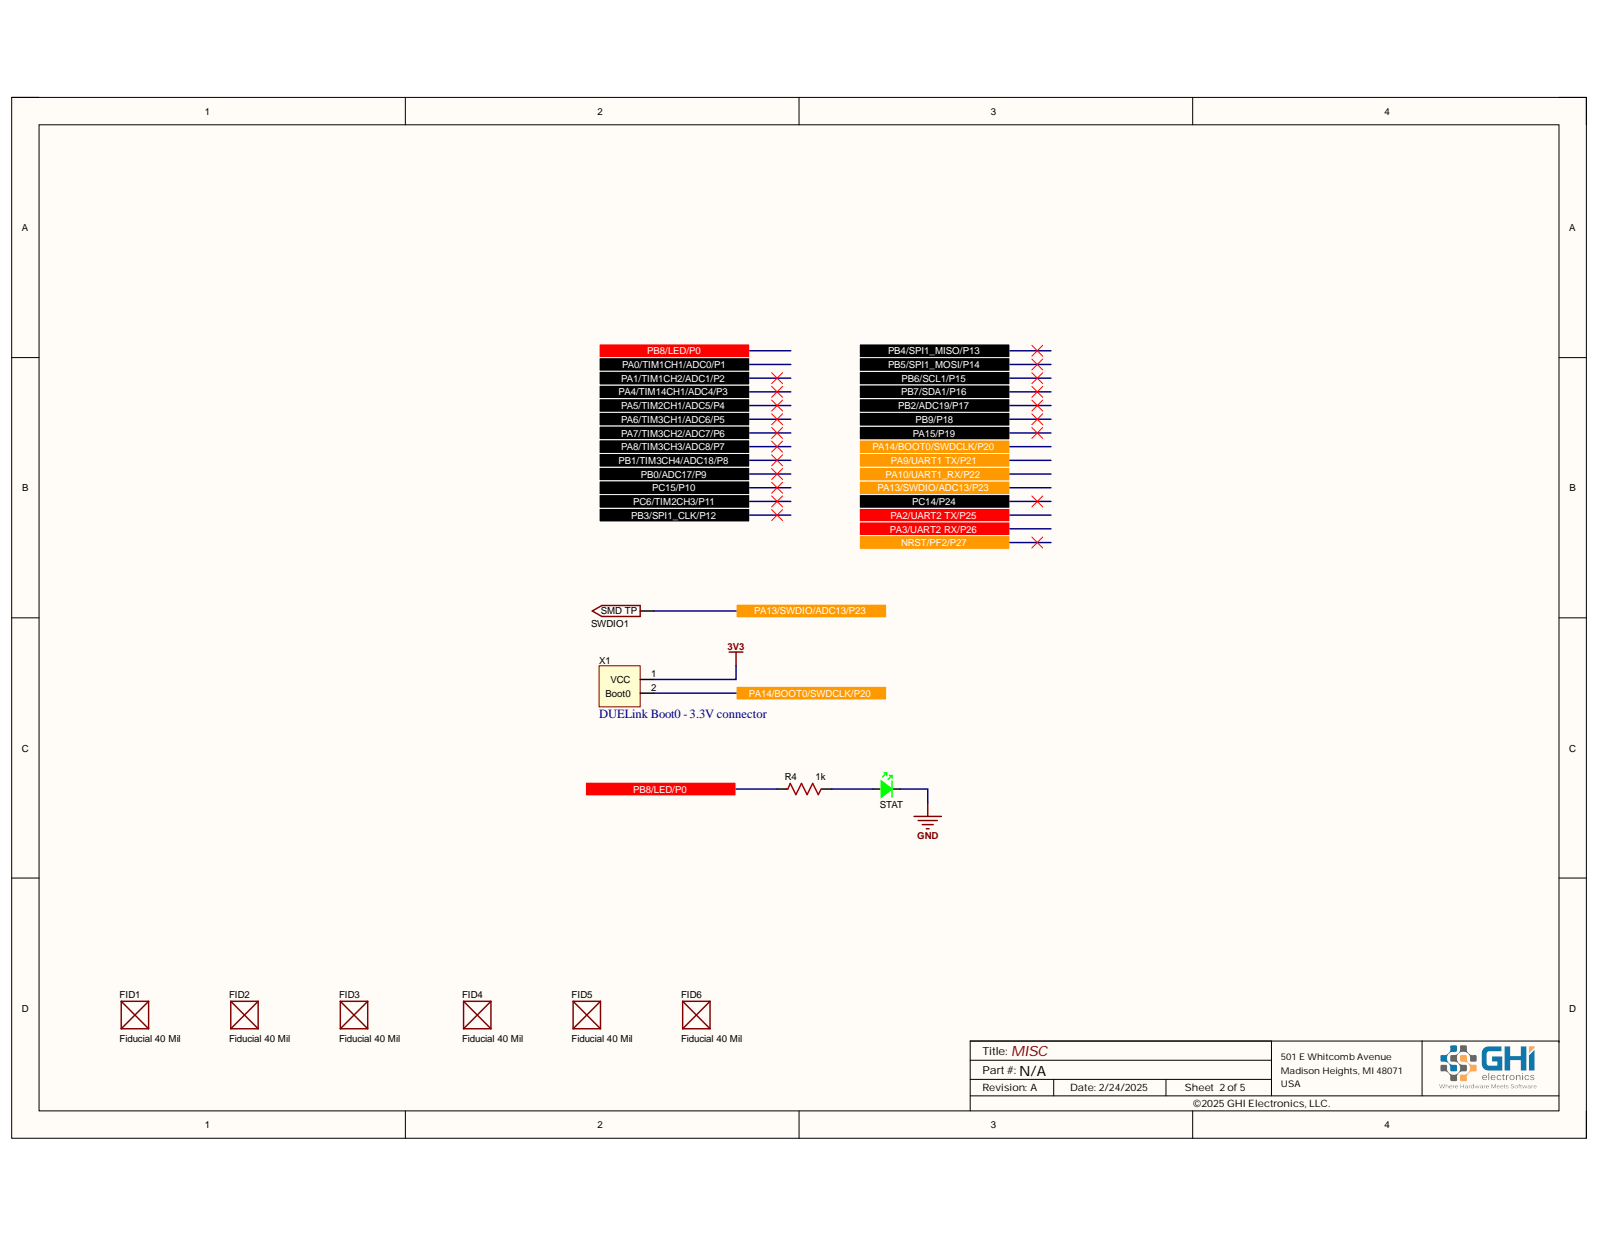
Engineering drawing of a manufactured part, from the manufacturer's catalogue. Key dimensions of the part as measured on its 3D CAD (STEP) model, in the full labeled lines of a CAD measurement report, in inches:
Part name (STEP PRODUCT): PCB; Board; LIGHT; User Library-LTST-C190TBKT (+7 more)
STEP written by: Open CASCADE 7.5 (AUTOMOTIVE_DESIGN)
Units: inches
Bodies: 91 solids, 1417 faces (1070 planar, 218 cylindrical, 129 other)
Overall size (bounding box): 0.748 × 0.669 × 0.272
Volume: 0.035 in³ · Surface area: 2.023 in²
Round holes (diameter × count): ⌀0.04 ×2, ⌀0.118 ×2
Partial cylindrical surfaces — rounded edges, fillets, slot ends (radius × count): R0.005 ×35, R0.006 ×14, R0.007 ×4, R0.007 ×4, R0.007 ×4, R0.059 ×2, R0.138 ×2
Main face-to-face distances: 0.063, 0.022, 0.018, 0.1, 0.517, 0.648, 0.073, 0.039, 0.207, 0.121
Hole centre spacings: 0.531, 0.1, 0.394, 0.631, 0.691
